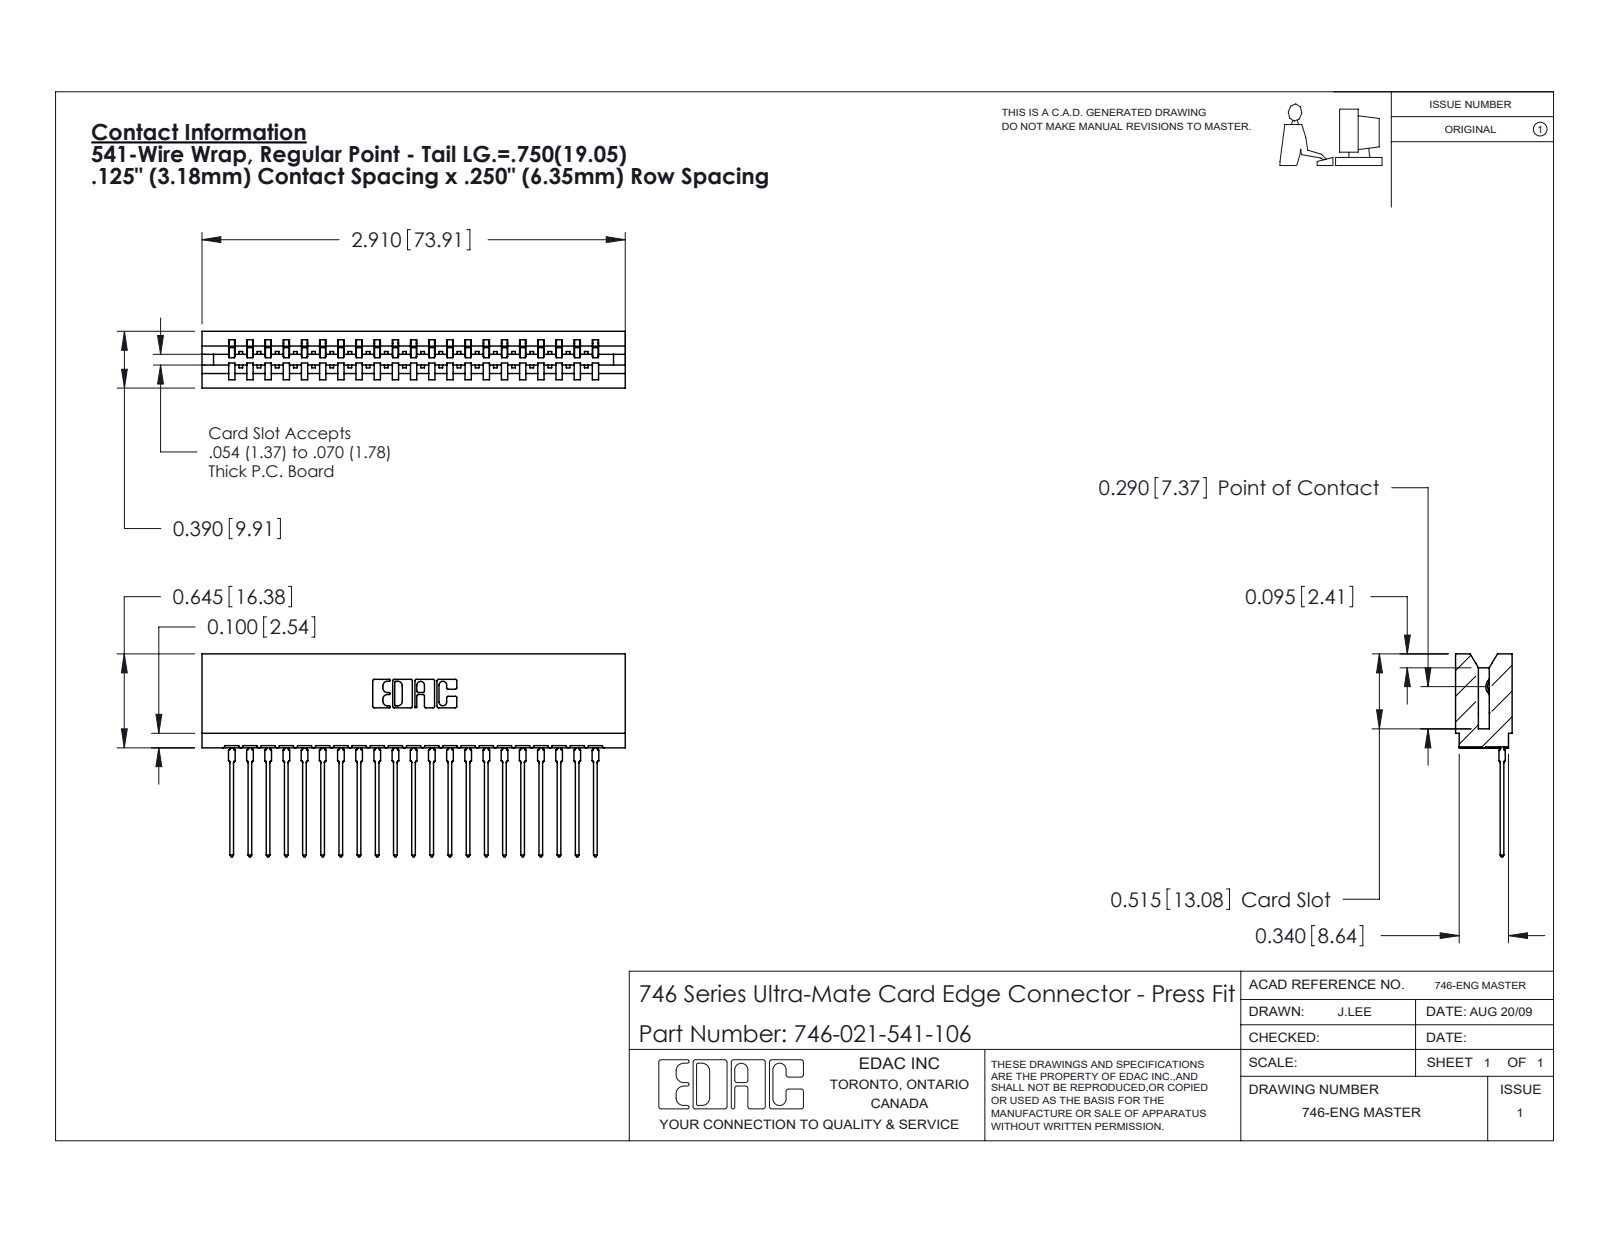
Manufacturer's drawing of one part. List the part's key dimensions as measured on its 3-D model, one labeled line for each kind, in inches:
Part name (STEP PRODUCT): 746-021-541-106; 746-292-001_541; 746 Part_.515 Slot Depth - 06
STEP written by: SolidWorks 2020 (CONFIG_CONTROL_DESIGN)
Units: inches
Bodies: 22 solids, 2366 faces (1379 planar, 441 cylindrical, 546 other)
Overall size (bounding box): 2.91 × 1.394 × 0.39
Volume: 0.485 in³ · Surface area: 18.51 in²
Partial cylindrical surfaces — rounded edges, fillets, slot ends (radius × count): R0.021 ×42, R0.01 ×22, R0.015 ×22, R0.007 ×6, R0.031 ×6, R0.005 ×4, R0.011 ×4, R0.026 ×3
Main face-to-face distances: 0.057, 0.333, 0.25, 0.39, 0.5, 0.025, 0.307, 0.083, 0.042, 0.125
